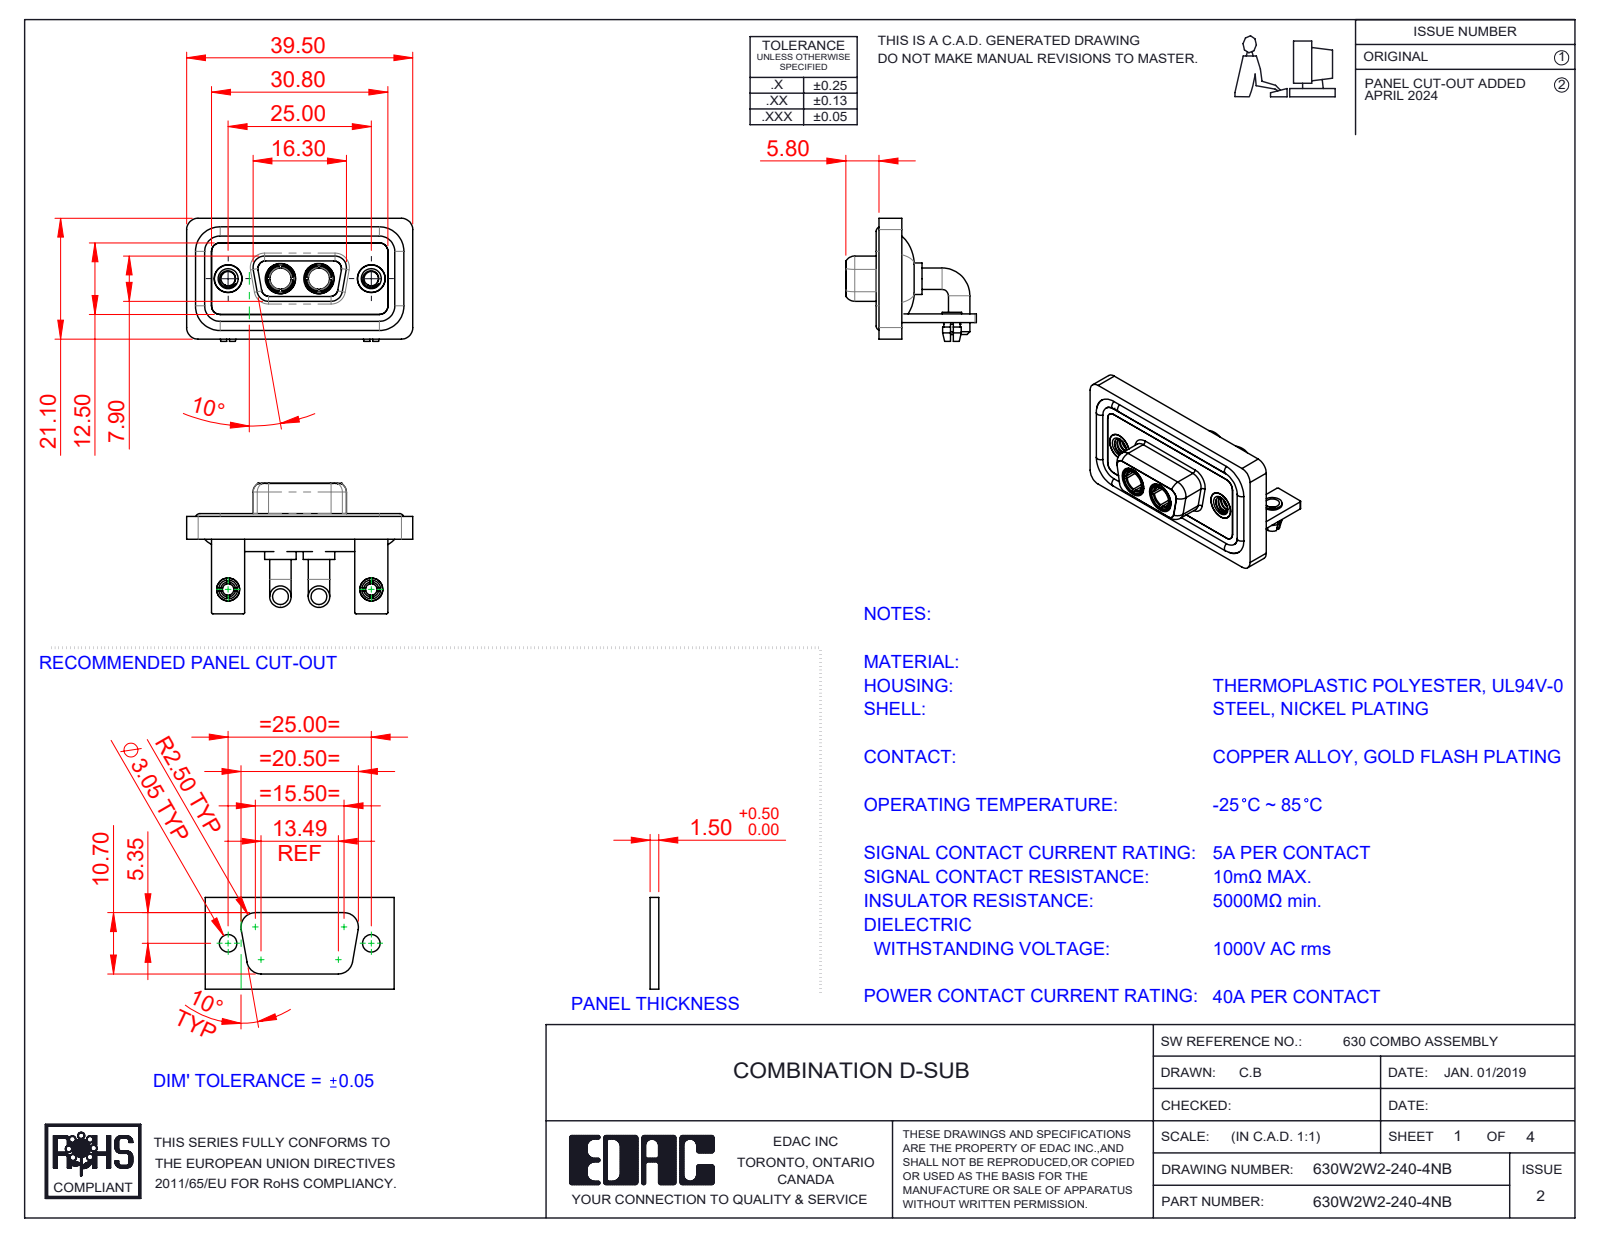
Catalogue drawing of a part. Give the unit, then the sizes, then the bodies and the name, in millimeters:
Units: millimetres
Overall size (bounding box): 39.5 × 22.8 × 21.5
Round holes (diameter × count): ⌀2.5 ×4, ⌀4.85 ×4, ⌀2 ×2, ⌀3.2 ×2, ⌀3.7 ×2, ⌀4 ×2, ⌀4.05 ×2, ⌀5 ×2, ⌀5.3 ×2
Round bosses / shafts (diameter × count): ⌀3.75 ×4, ⌀1.6 ×4, ⌀5.5 ×2, ⌀5.2 ×2, ⌀4.96 ×2, ⌀4.95 ×2, ⌀4.8 ×2, ⌀4.75 ×2
Partial cylindrical surfaces — rounded edges, fillets, slot ends (radius × count): R2 ×19, R1.5 ×18, R0.25 ×16, R1.35 ×8, R1.6 ×8, R0.5 ×5, R0.6 ×4, R0.65 ×4
Main face-to-face distances: 0.4, 2.9, 1.5, 1.8, 1.1, 3.7, 0.8, 2.5, 1.6, 3.1
Hole centre spacings: 9.14, 15.86, 25, 6.72
Volume: 5 357 mm³ · Surface area: 8 822 mm²
Bodies: 15 solids, 676 faces (231 planar, 292 cylindrical, 153 other)
Part name (STEP PRODUCT): 630Combo Stabilizer Bracket_50 Contacts; Power Socket_40A RA; 630Combo Shell Front_09 Contacts; 630Combo Threaded Rivet_A (+5 more)
STEP written by: SolidWorks 2023 (CONFIG_CONTROL_DESIGN)
